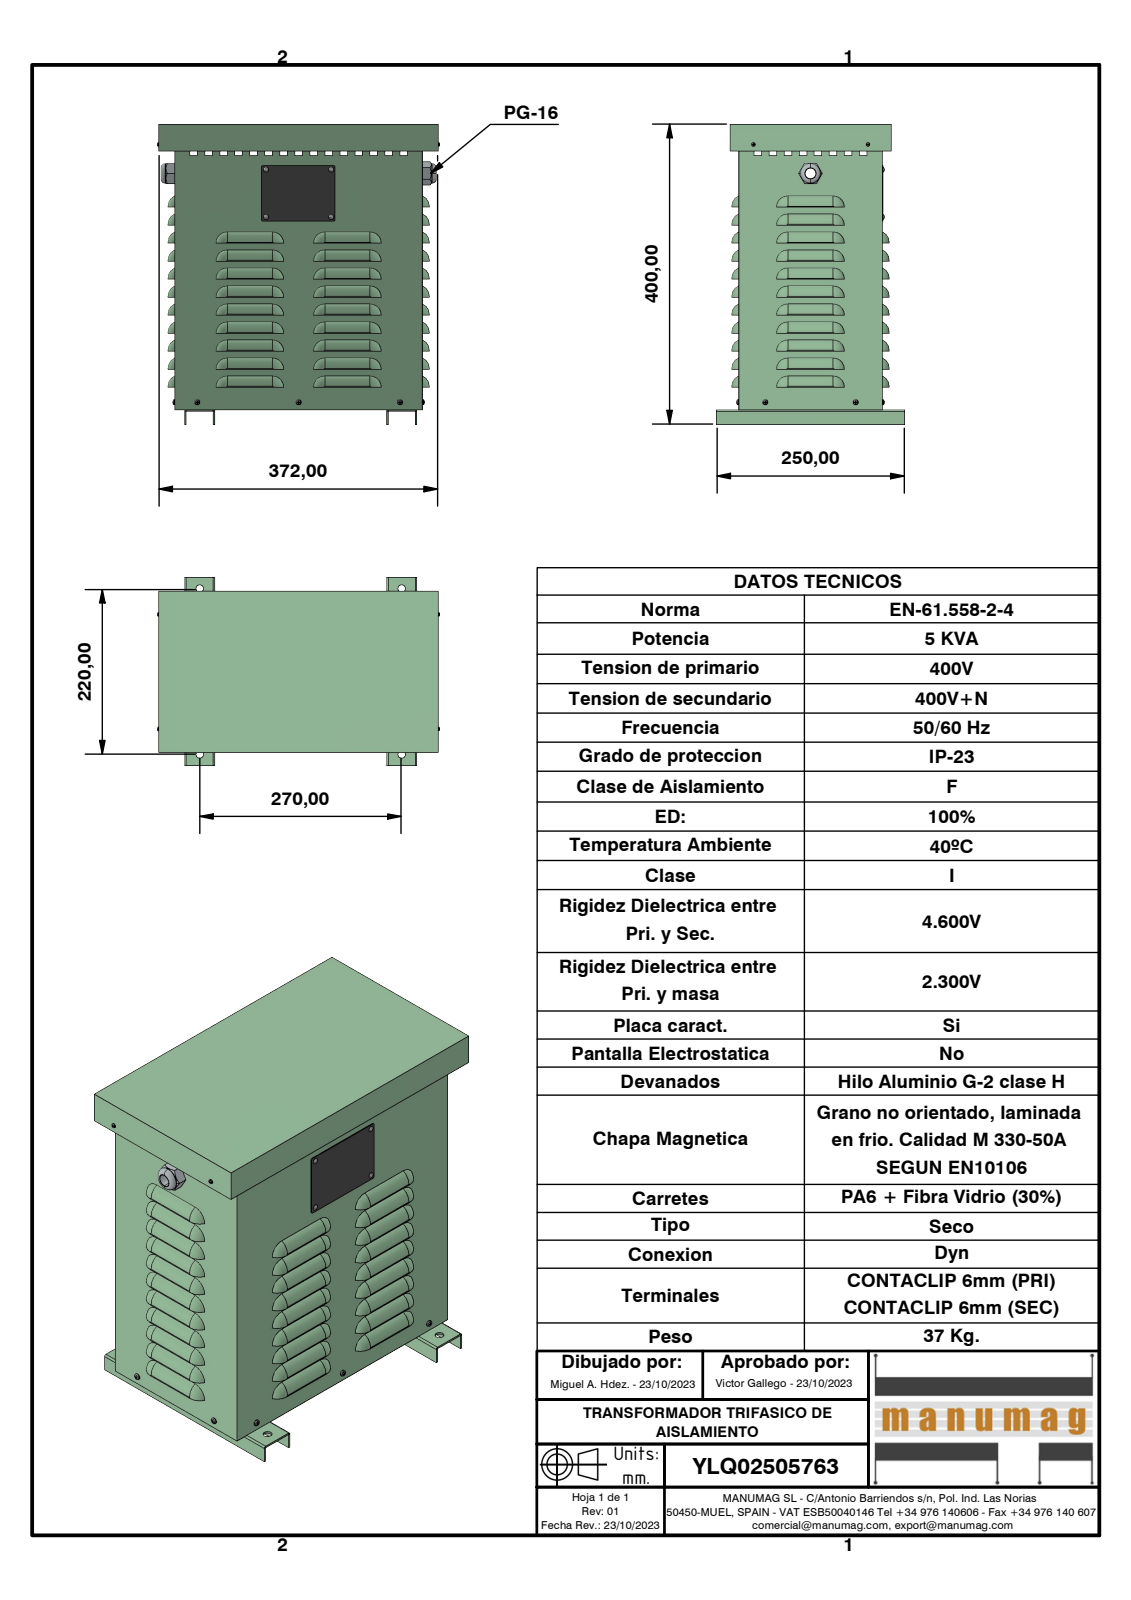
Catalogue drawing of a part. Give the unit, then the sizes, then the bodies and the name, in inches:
Units: inches
Overall size (bounding box): 15.773 × 14.809 × 9.843
Round holes (diameter × count): ⌀0.157 ×9, ⌀0.118 ×4, ⌀0.394 ×4, ⌀0.551 ×1, ⌀0.945 ×1
Round bosses / shafts (diameter × count): ⌀0.138 ×5, ⌀0.125 ×5, ⌀0.126 ×4, ⌀0.098 ×2, ⌀0.089 ×2, ⌀1.024 ×1, ⌀0.906 ×1, ⌀0.886 ×1
Partial cylindrical surfaces — rounded edges, fillets, slot ends (radius × count): R0.551 ×66, R0.276 ×42, R0.591 ×42, R0.059 ×12, R0.197 ×8, R0.217 ×8, R0.02 ×5, R0.02 ×4
Main face-to-face distances: 0.02, 7.5, 0.059, 7.48, 14.926, 12.972, 7.52, 14.985, 12.953, 12.992
Hole centre spacings: 2.48, 3.356, 3.425, 4.229, 5.315, 5.984, 8.661, 9.874
Volume: 53.89 in³ · Surface area: 2 086 in²
Bodies: 26 solids, 1888 faces (958 planar, 396 cylindrical, 534 other)
Part name (STEP PRODUCT): YLQ02505763; JE010 NACIONAL CUERPO; JE010 NACIONAL BASE; PLACA CARACTERISTICAS (+6 more)
STEP written by: Autodesk Inventor 2023 (AUTOMOTIVE_DESIGN)
